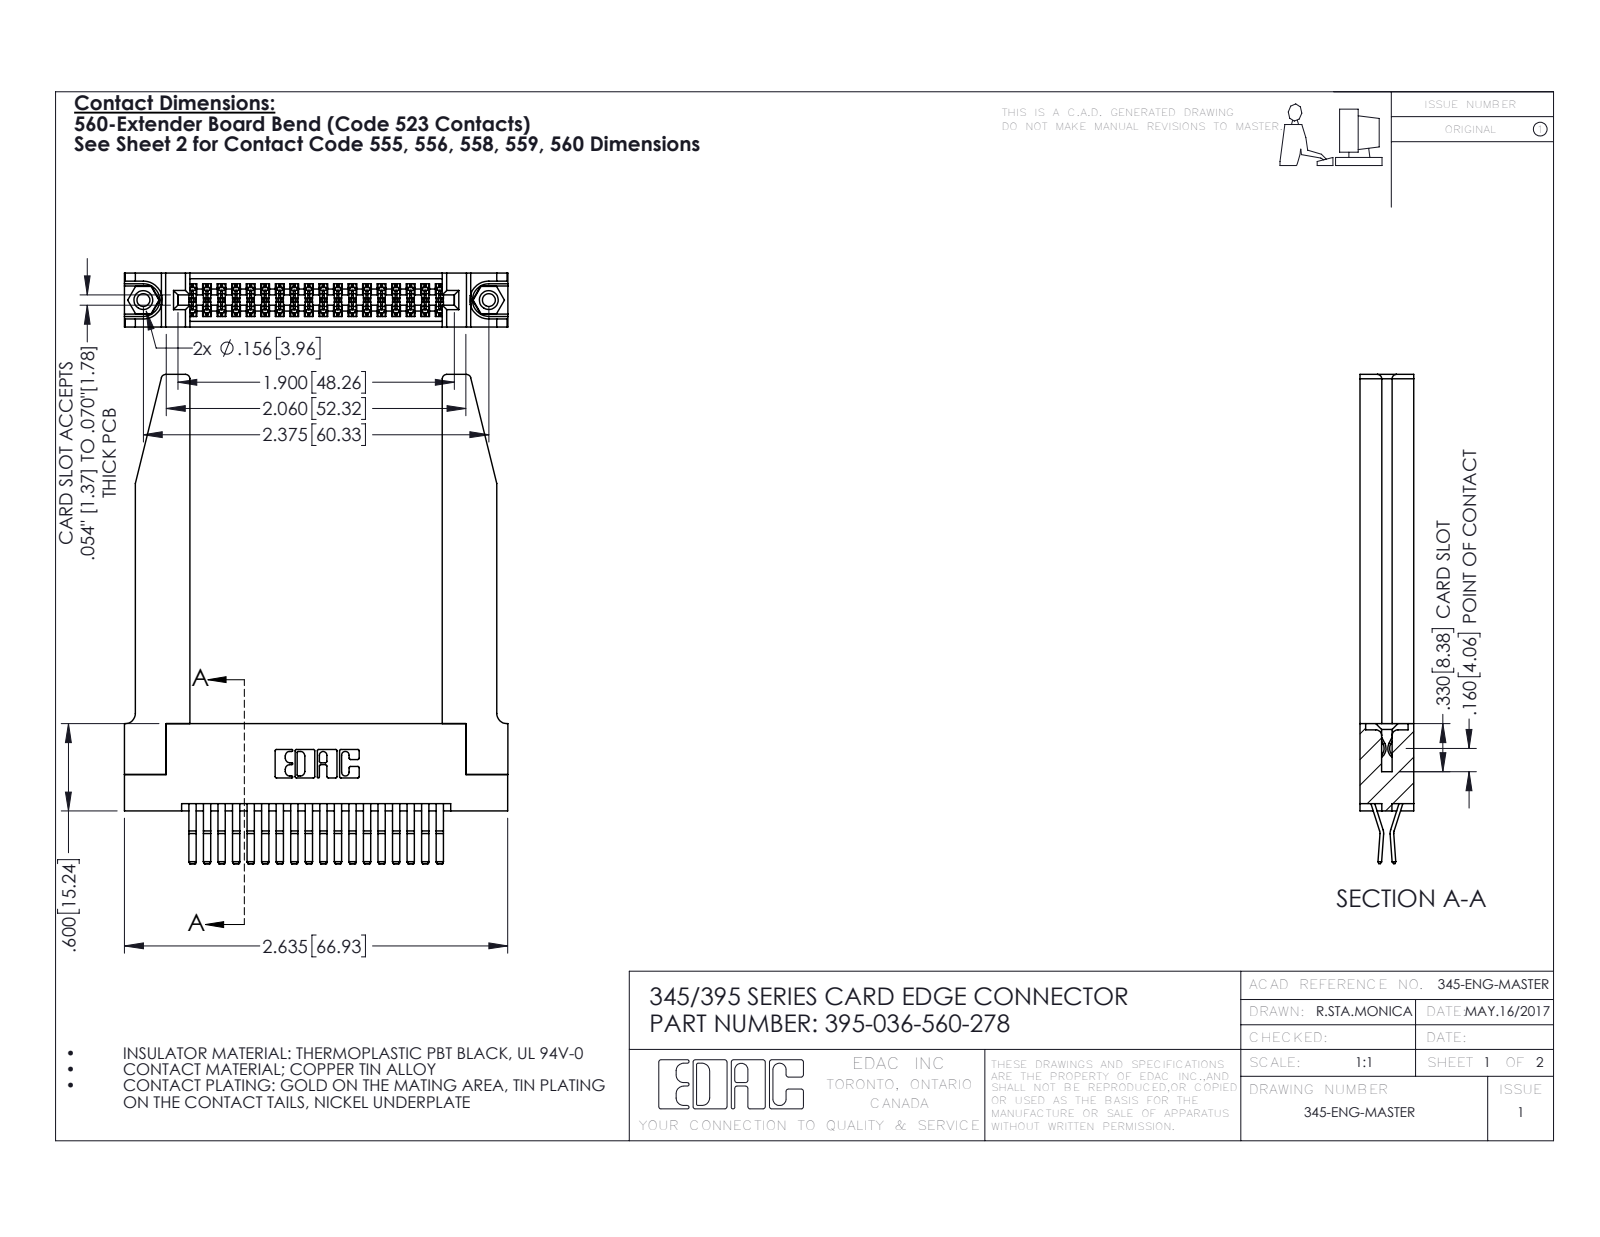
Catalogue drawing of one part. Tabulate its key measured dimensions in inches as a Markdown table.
| quantity | value |
| --- | --- |
| part name | 345-292-001_560 Tail; 345-250-001_345-250-001-102; 345 Part_Flush Mounting Lugs - 0.156 Dia-TH; 345-220-078_345-220-078 (+1 more) |
| STEP written by | SolidWorks 2016 (CONFIG_CONTROL_DESIGN) |
| units | inches |
| bodies | 41 solids, 2232 faces (1410 planar, 770 cylindrical, 52 other) |
| overall size | 3.362 × 2.636 × 0.37 |
| volume | 0.872 in³ |
| surface area | 25.75 in² |
| round holes (diameter × count) | 0.089 × 2, 0.125 × 2, 0.156 × 2, 0.064 × 1 |
| round bosses / shafts (diameter × count) | 0.155 × 2 |
| partial cylindrical surfaces (radius × count) | 0.006 × 54, 0.01 × 22, 0.03 × 8, 0.007 × 6, 0.031 × 6, 0.026 × 3, 0.01 × 2, 0.014 × 2 |
| main face-to-face distances | 0.37, 0.072, 0.298, 0.025, 0.2, 0.15, 0.148, 0.098, 0.272, 0.225 |
| hole center spacings | 0.27, 2.141, 2.375 |
